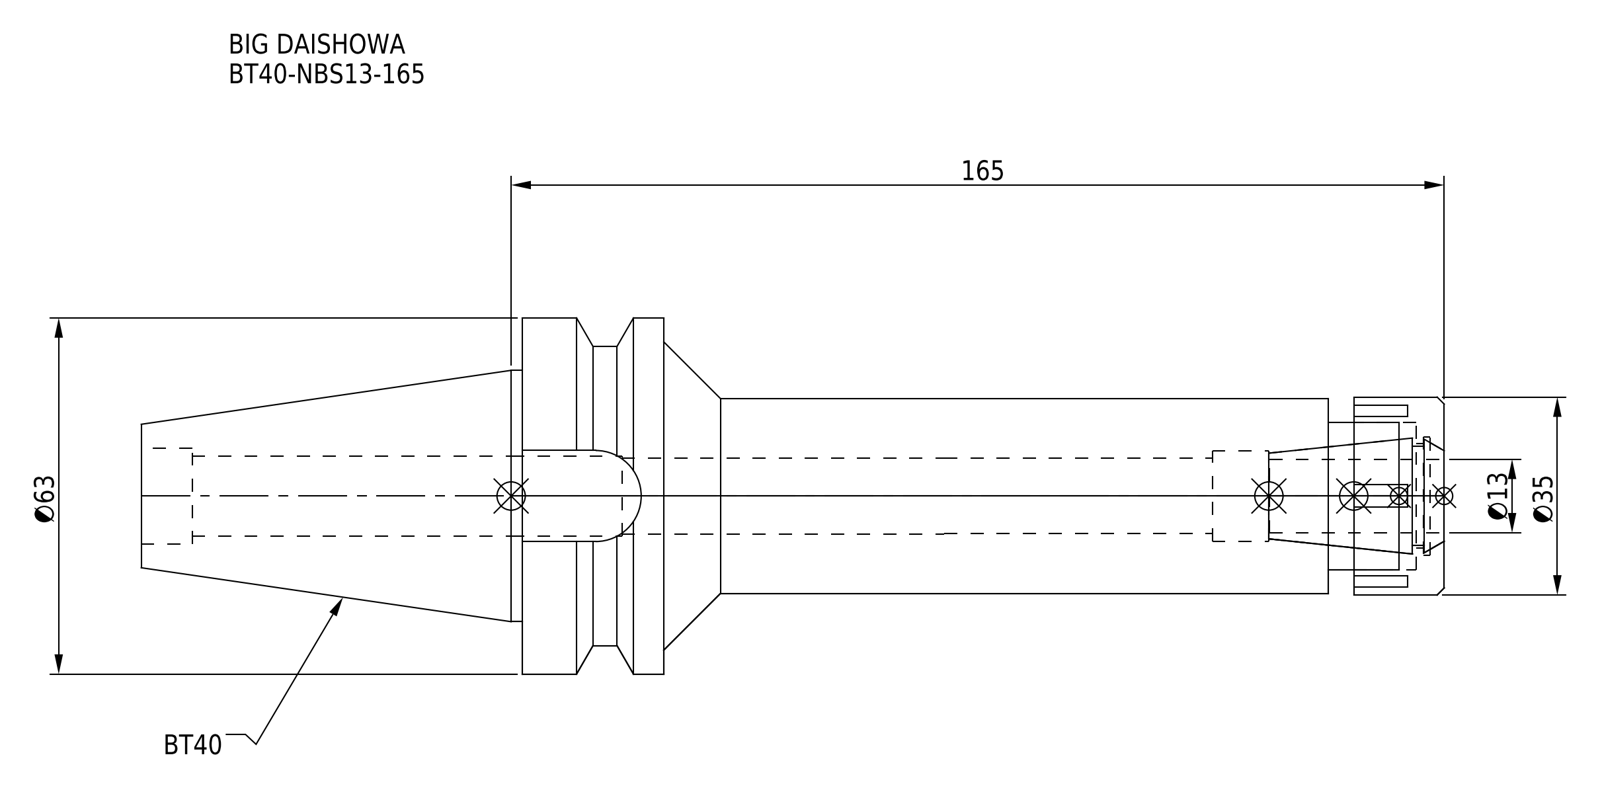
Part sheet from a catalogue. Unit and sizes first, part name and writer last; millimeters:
Units: millimetres
Overall size (bounding box): 230.4 × 63 × 63
Round holes (diameter × count): ⌀13.3 ×1, ⌀13.5 ×1, ⌀14.2 ×1, ⌀16 ×1, ⌀17 ×1, ⌀18.5 ×1, ⌀21 ×1, ⌀26 ×1
Round bosses / shafts (diameter × count): ⌀63 ×1, ⌀53 ×1, ⌀44.45 ×1, ⌀35 ×1, ⌀34.5 ×1
Partial cylindrical surfaces — rounded edges, fillets, slot ends (radius × count): R8.05 ×1
Main face-to-face distances: 25, 138, 163, 20.5, 122, 8, 117.5, 142.5, 16, 4.5
Volume: 228 328 mm³ · Surface area: 46 410 mm²
Bodies: 2 solids, 93 faces (45 planar, 34 cylindrical, 14 other)
Part name (STEP PRODUCT): DXF_TEMP_ASSY_ASM_4_ASM.stp; BT40-NBS13-165-FreeParts; BT40-NBS13-165_1.stp; NBN13_1.stp (+3 more)
STEP written by: SolidWorks 2019 (CONFIG_CONTROL_DESIGN)
